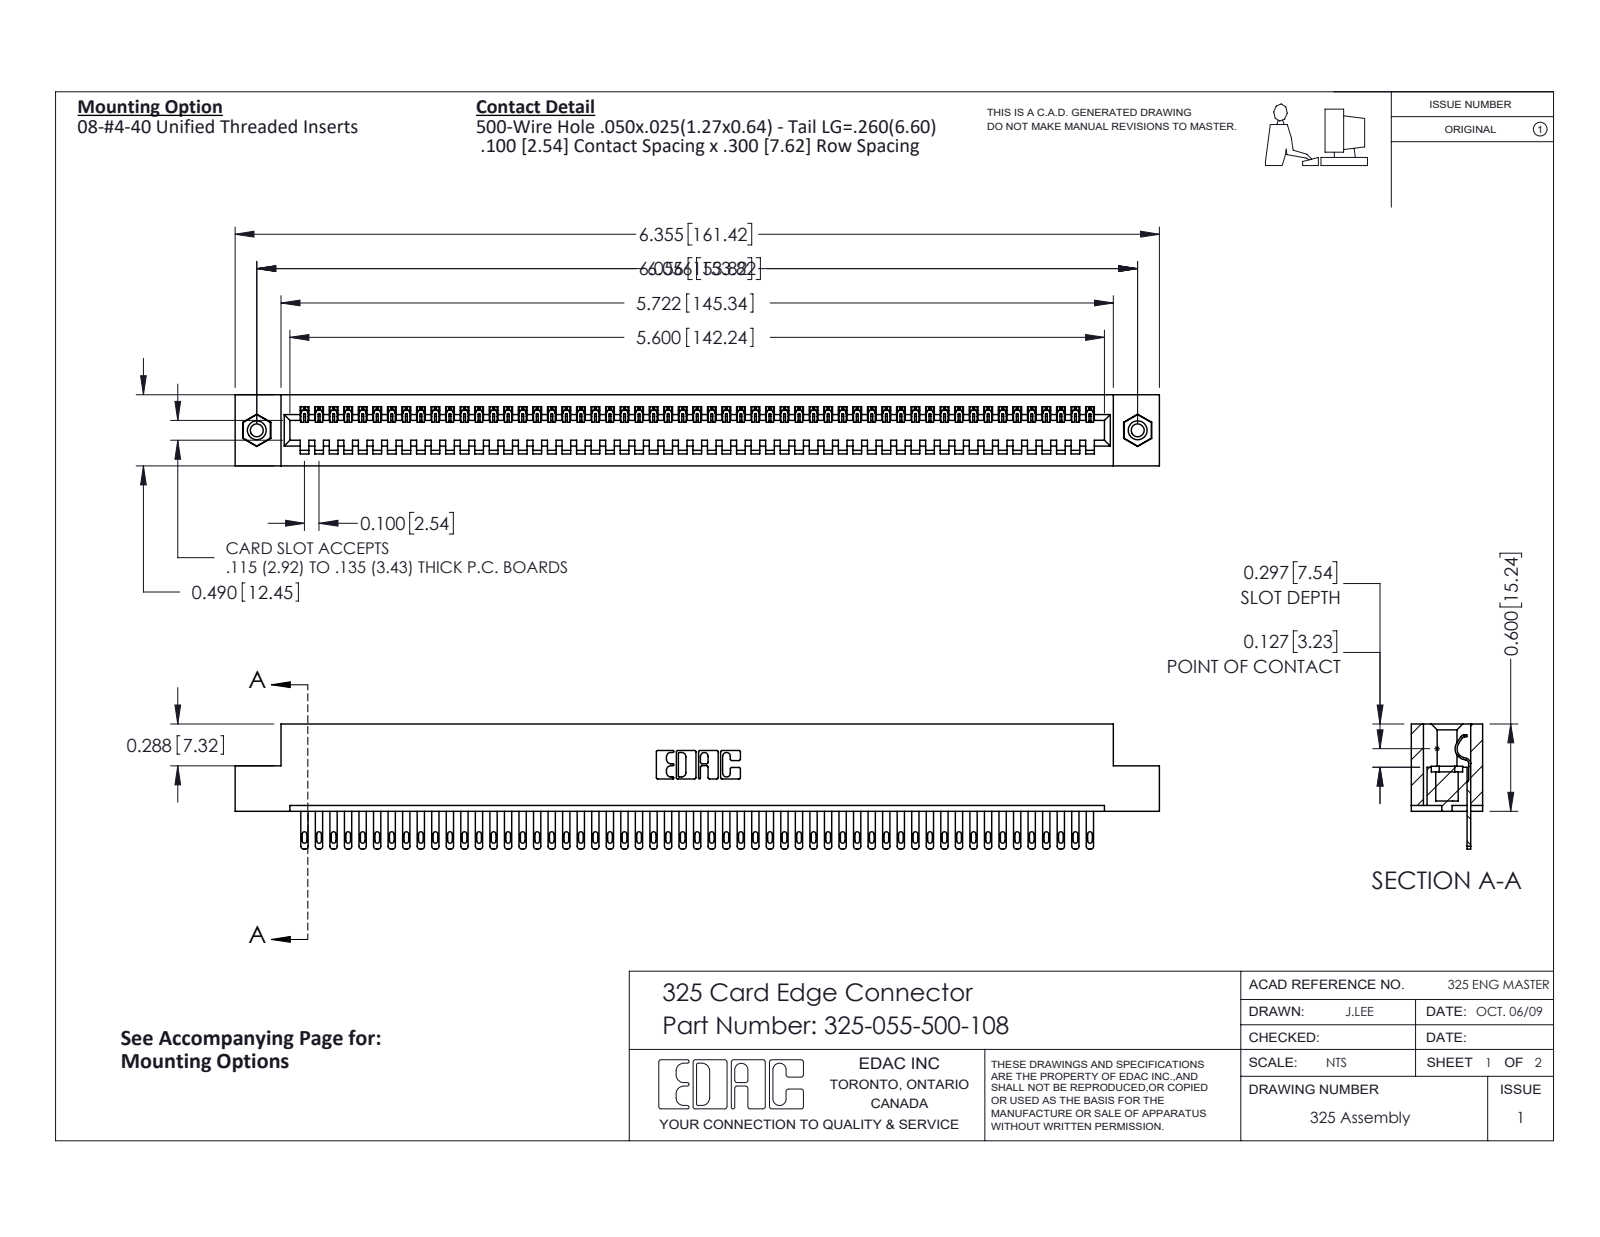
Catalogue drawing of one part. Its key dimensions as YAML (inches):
part_name: "345-250-001_345-250-003-102; 325 Part_TI; 325-292-001_325-293-100; 325-055-500-108"
step_written_by: "SolidWorks 2016 (CONFIG_CONTROL_DESIGN)"
units: inches
bodies: {solids: 58, faces: 3144, planar: 2082, cylindrical: 1046, other: 16}
overall_size: [6.355, 0.86, 0.49]
volume: 1.258
surface_area: 35.49
round_holes:
  - {diameter: 0.089, count: 2}
  - {diameter: 0.125, count: 2}
  - {diameter: 0.16, count: 2}
round_bosses_or_shafts:
  - {diameter: 0.155, count: 2}
partial_cylinders:
  - {radius: 0.006, count: 110}
  - {radius: 0.016, count: 110}
  - {radius: 0.02, count: 110}
  - {radius: 0.01, count: 22}
  - {radius: 0.007, count: 6}
  - {radius: 0.031, count: 6}
  - {radius: 0.026, count: 3}
  - {radius: 0.014, count: 1}
face_to_face_distances: [0.083, 0.407, 0.49, 0.3, 0.107, 0.383, 0.025, 0.325, 0.263, 0.56]
hole_center_spacings: [6.056]
